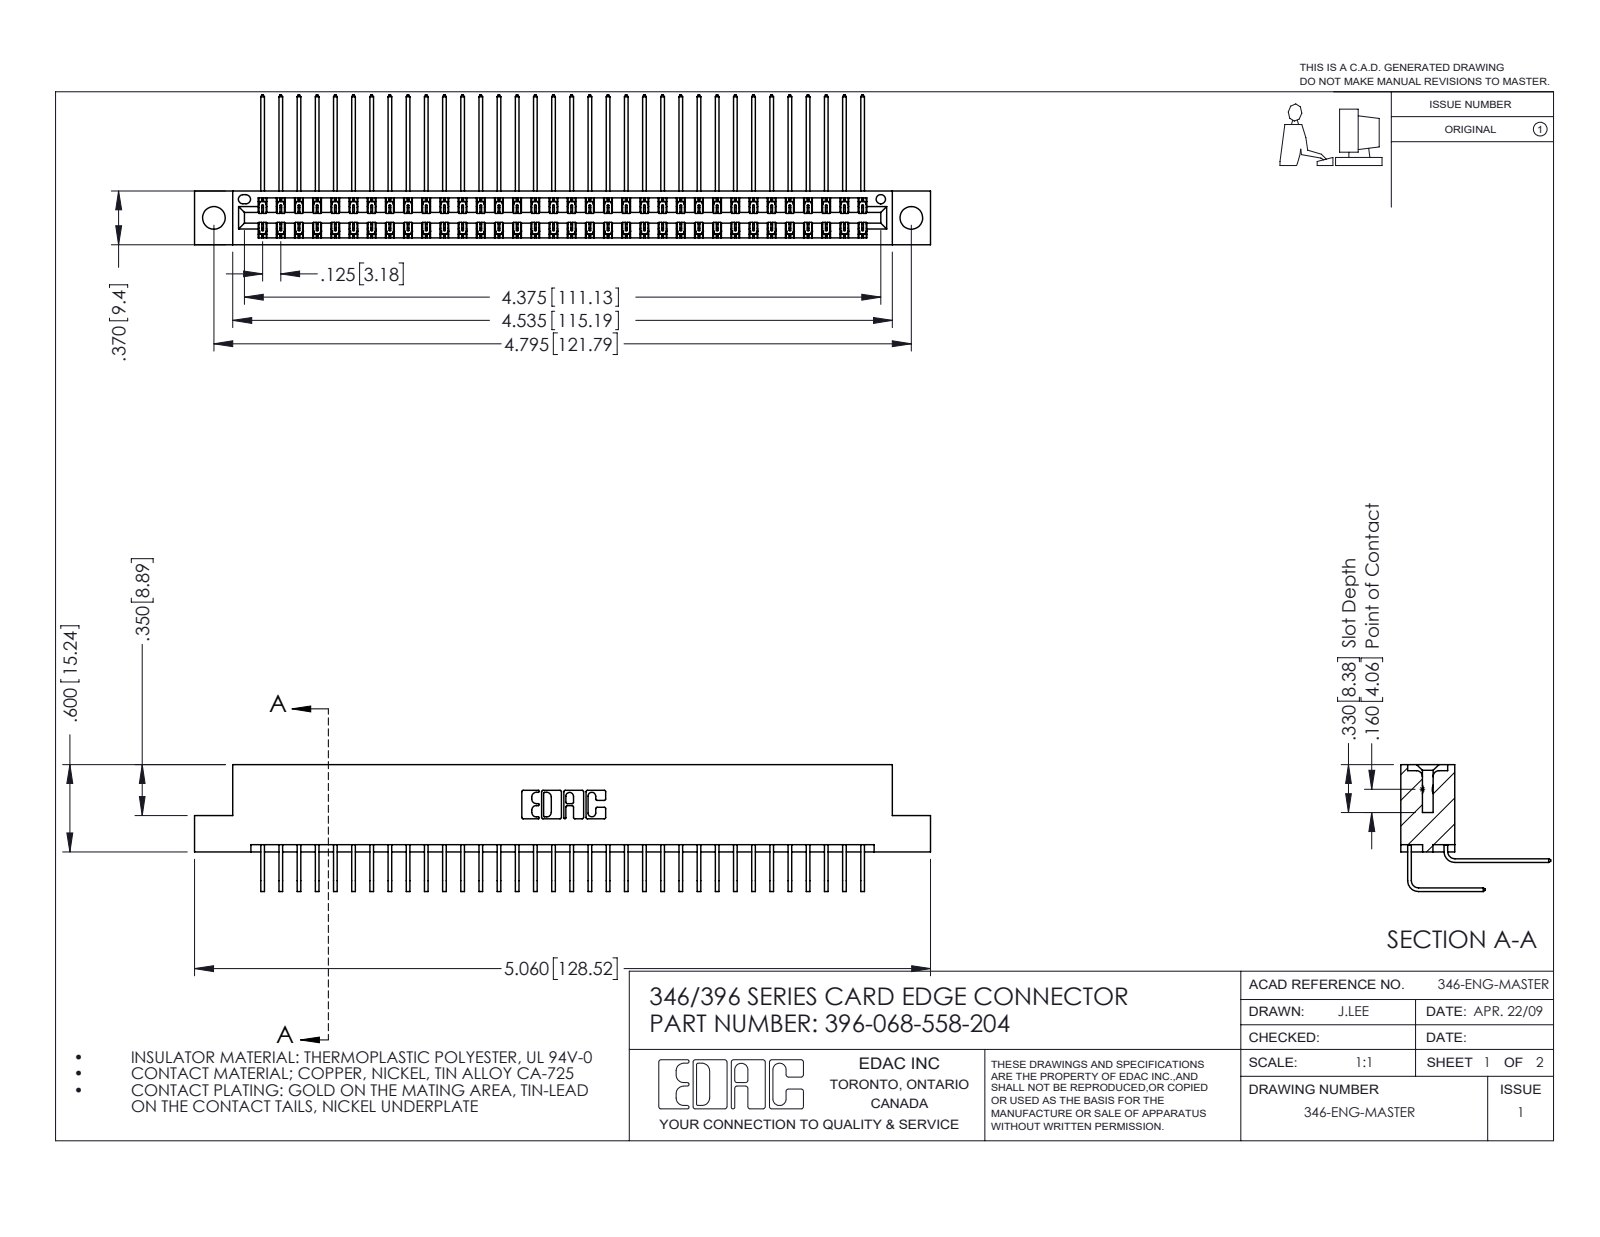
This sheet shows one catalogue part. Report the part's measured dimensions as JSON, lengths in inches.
{"part_name": "345-292-001_558 559 Tail - 1; 396-068-558-204; 346 Part_Flush Mounting Lugs - 0.156 Dia-TH; 345-292-001_558 Tail - 2", "step_written_by": "SolidWorks 2016 (CONFIG_CONTROL_DESIGN)", "units": "inches", "bodies": {"solids": 69, "faces": 3794, "planar": 2592, "cylindrical": 1202, "other": 0}, "overall_size": [5.06, 1.03, 0.873], "volume_in3": 0.78, "surface_area_in2": 29.65, "round_holes": [[0.156, 2], [0.064, 1]], "partial_cylinders_radius": [[0.006, 102], [0.01, 22], [0.007, 6], [0.031, 6], [0.026, 3], [0.014, 2], [0.022, 2], [0.024, 2]], "face_to_face_distances": [0.048, 0.322, 0.025, 0.25, 0.37, 0.072, 0.298, 0.275, 0.148, 0.222], "hole_center_spacings": [0.246, 4.587, 4.795]}
